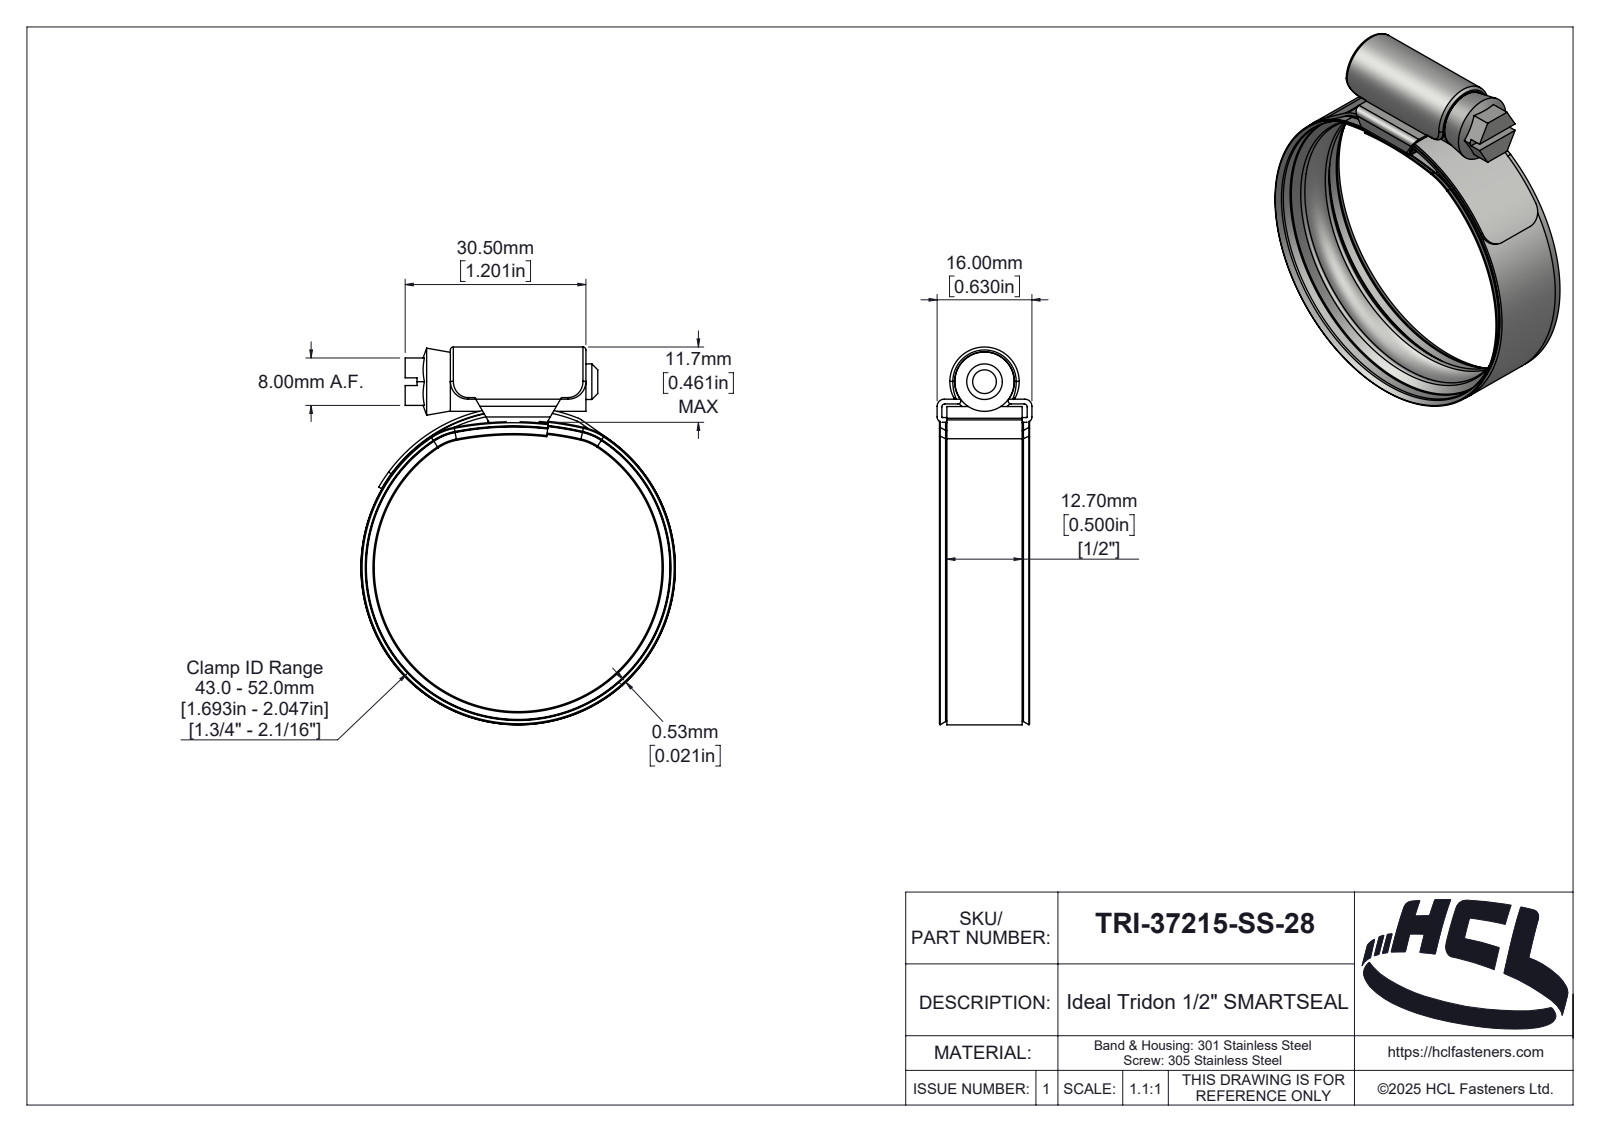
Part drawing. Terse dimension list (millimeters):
name: TRI-37215-SS-28
written by: SolidWorks 2025 (AUTOMOTIVE_DESIGN)
unit: mm
bodies: 4 solids, 418 faces (42 planar, 119 cylindrical, 257 other)
size: 63.73 × 53.06 × 16
volume: 4 927 mm³; area: 13 858 mm²
holes: 1× ⌀51.4, 1× ⌀52
bosses: 1× ⌀53.06, 1× ⌀51.8, 1× ⌀10, 1× ⌀6
rounds: 6× R0.5, 4× R3, 2× R0.1, 2× R0.9, 2× R1.2, 2× R9.9, 2× R10.1, 1× R0.46
face distances: 0.8, 3.1, 12.7, 2.3, 0.53, 30.5, 3.9, 1.65, 14.35, 15.2
